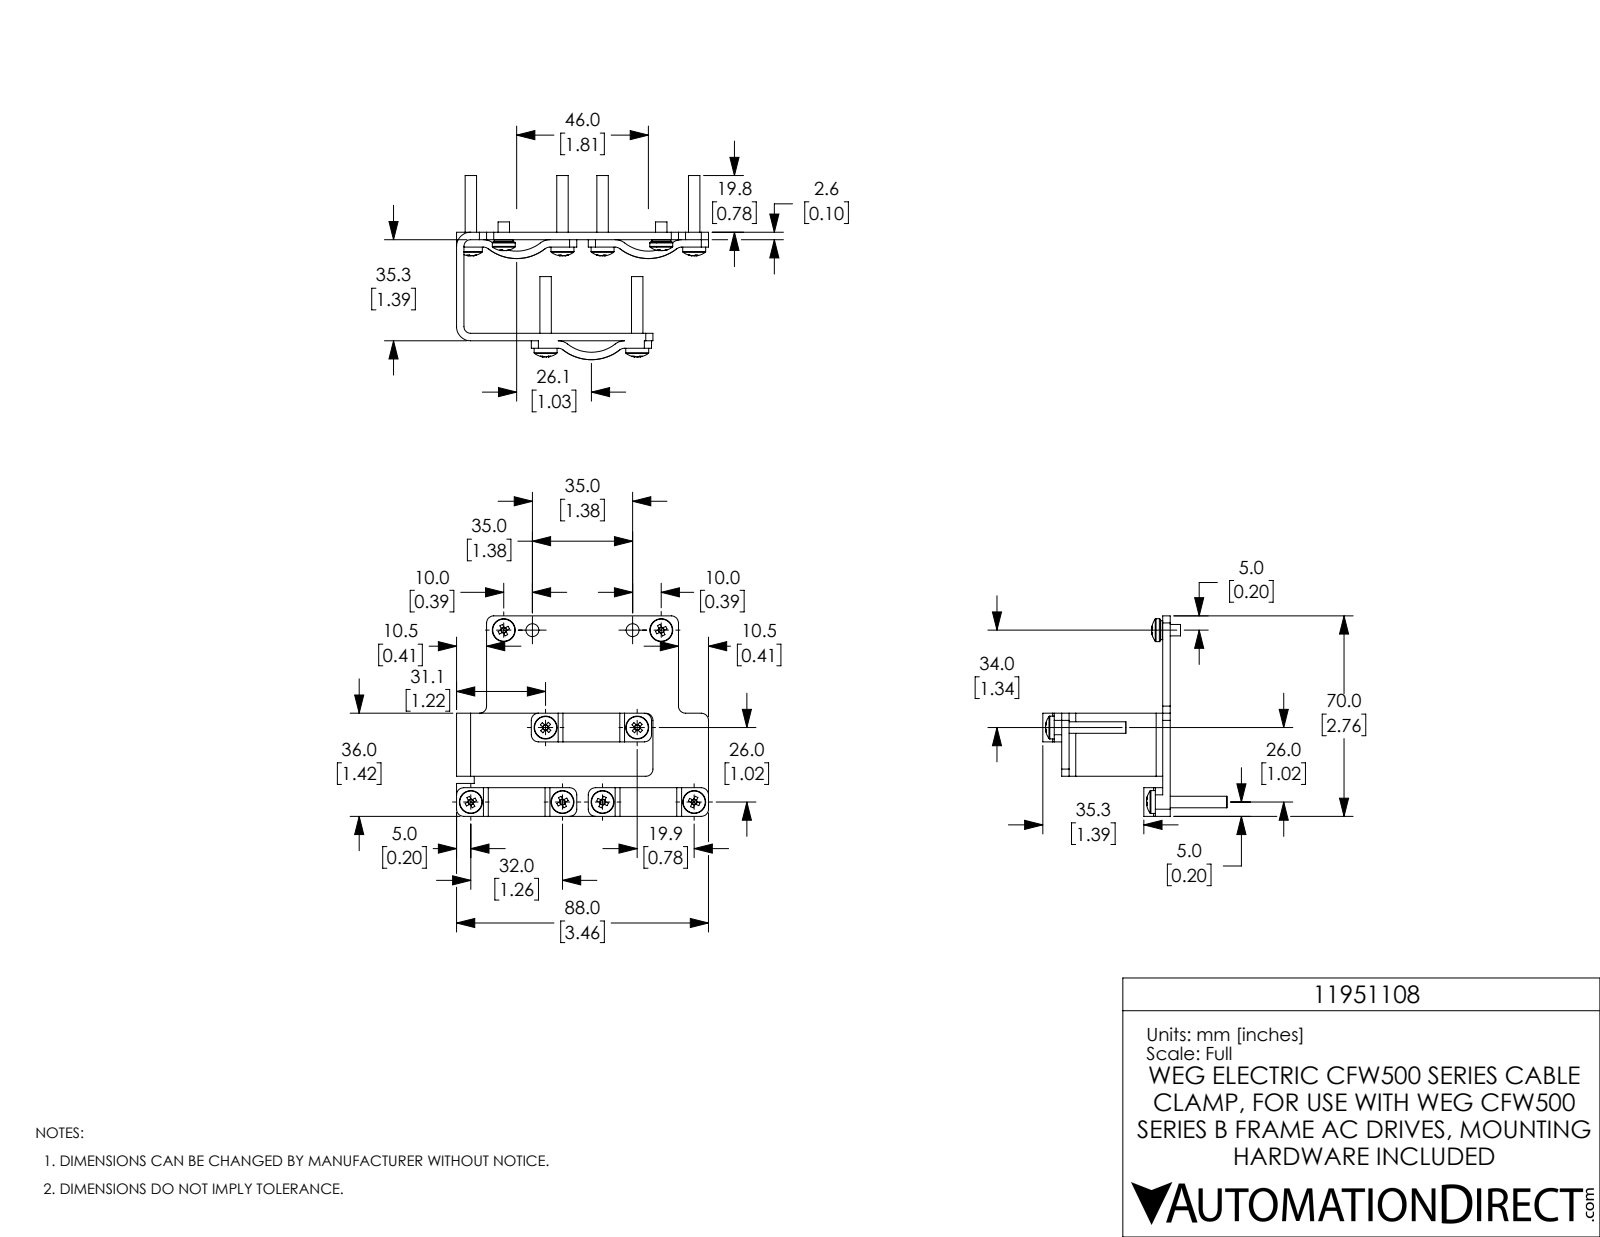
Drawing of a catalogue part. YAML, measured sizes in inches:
part_name: "ZBC_10006124392 nc cmb1"
step_written_by: "SolidWorks 2017 (AUTOMOTIVE_DESIGN)"
units: inches
bodies: {solids: 1, faces: 422, planar: 191, cylindrical: 121, other: 110}
overall_size: [3.465, 2.756, 2.531]
volume: 1.555
surface_area: 33.54
round_holes:
  - {diameter: 0.177, count: 8}
  - {diameter: 0.13, count: 2}
  - {diameter: 0.148, count: 2}
round_bosses_or_shafts:
  - {diameter: 0.315, count: 8}
  - {diameter: 0.157, count: 8}
  - {diameter: 0.26, count: 2}
  - {diameter: 0.126, count: 2}
partial_cylinders:
  - {radius: 0.098, count: 19}
  - {radius: 0.106, count: 6}
  - {radius: 0.209, count: 6}
  - {radius: 0.531, count: 3}
  - {radius: 0.634, count: 3}
  - {radius: 0.091, count: 2}
  - {radius: 0.193, count: 2}
face_to_face_distances: [0.102, 1.39, 1.287, 1.492, 1.417, 0.394, 1.024, 0.551, 0.866, 0.205]
hole_center_spacings: [1.26, 0.394, 1.289, 1.45, 1.772, 1.811, 2.398, 2.405]
